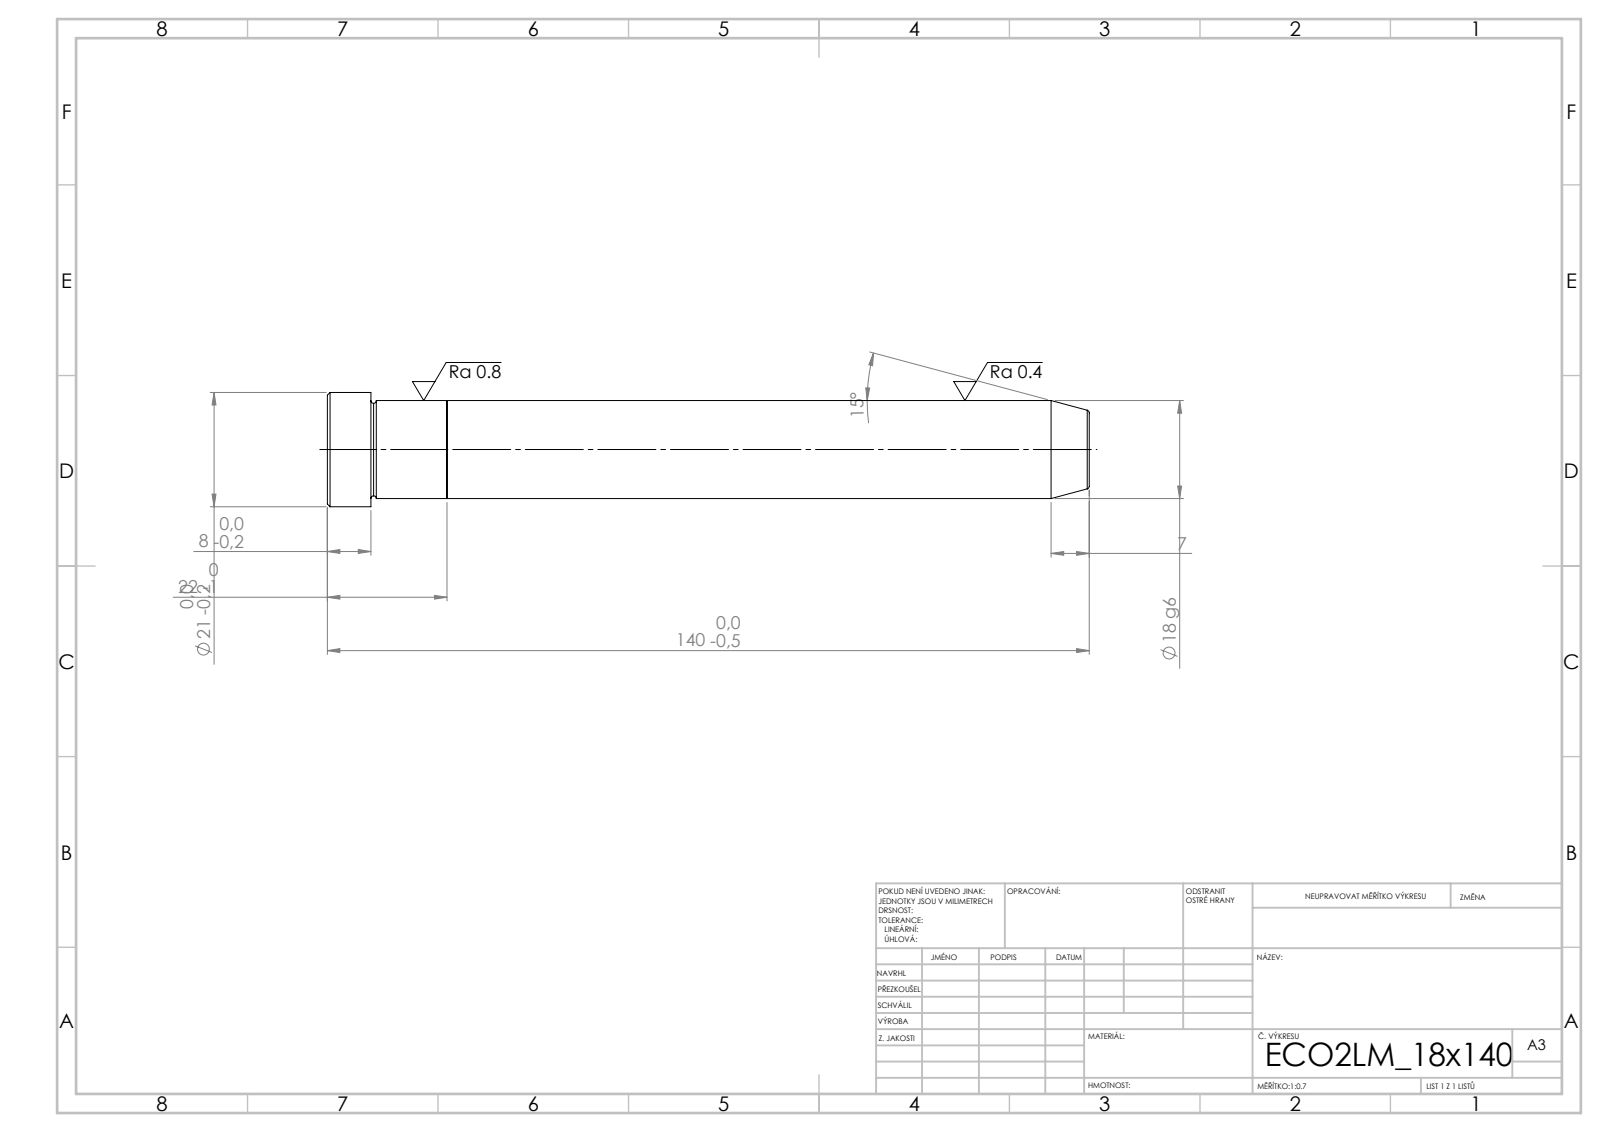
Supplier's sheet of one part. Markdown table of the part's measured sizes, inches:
| quantity | value |
| --- | --- |
| STEP written by | SolidWorks 2019 (CONFIG_CONTROL_DESIGN) |
| units | inches |
| bodies | 2 solids, 21 faces (5 planar, 6 cylindrical, 10 other) |
| overall size | 5.512 × 0.827 × 0.827 |
| volume | 2.196 in³ |
| surface area | 14.06 in² |
| round bosses / shafts (diameter × count) | 0.827 × 1, 0.709 × 1 |
| main face-to-face distances | 0.866, 4.646, 5.512, 5.197, 0.551, 0.315 |
